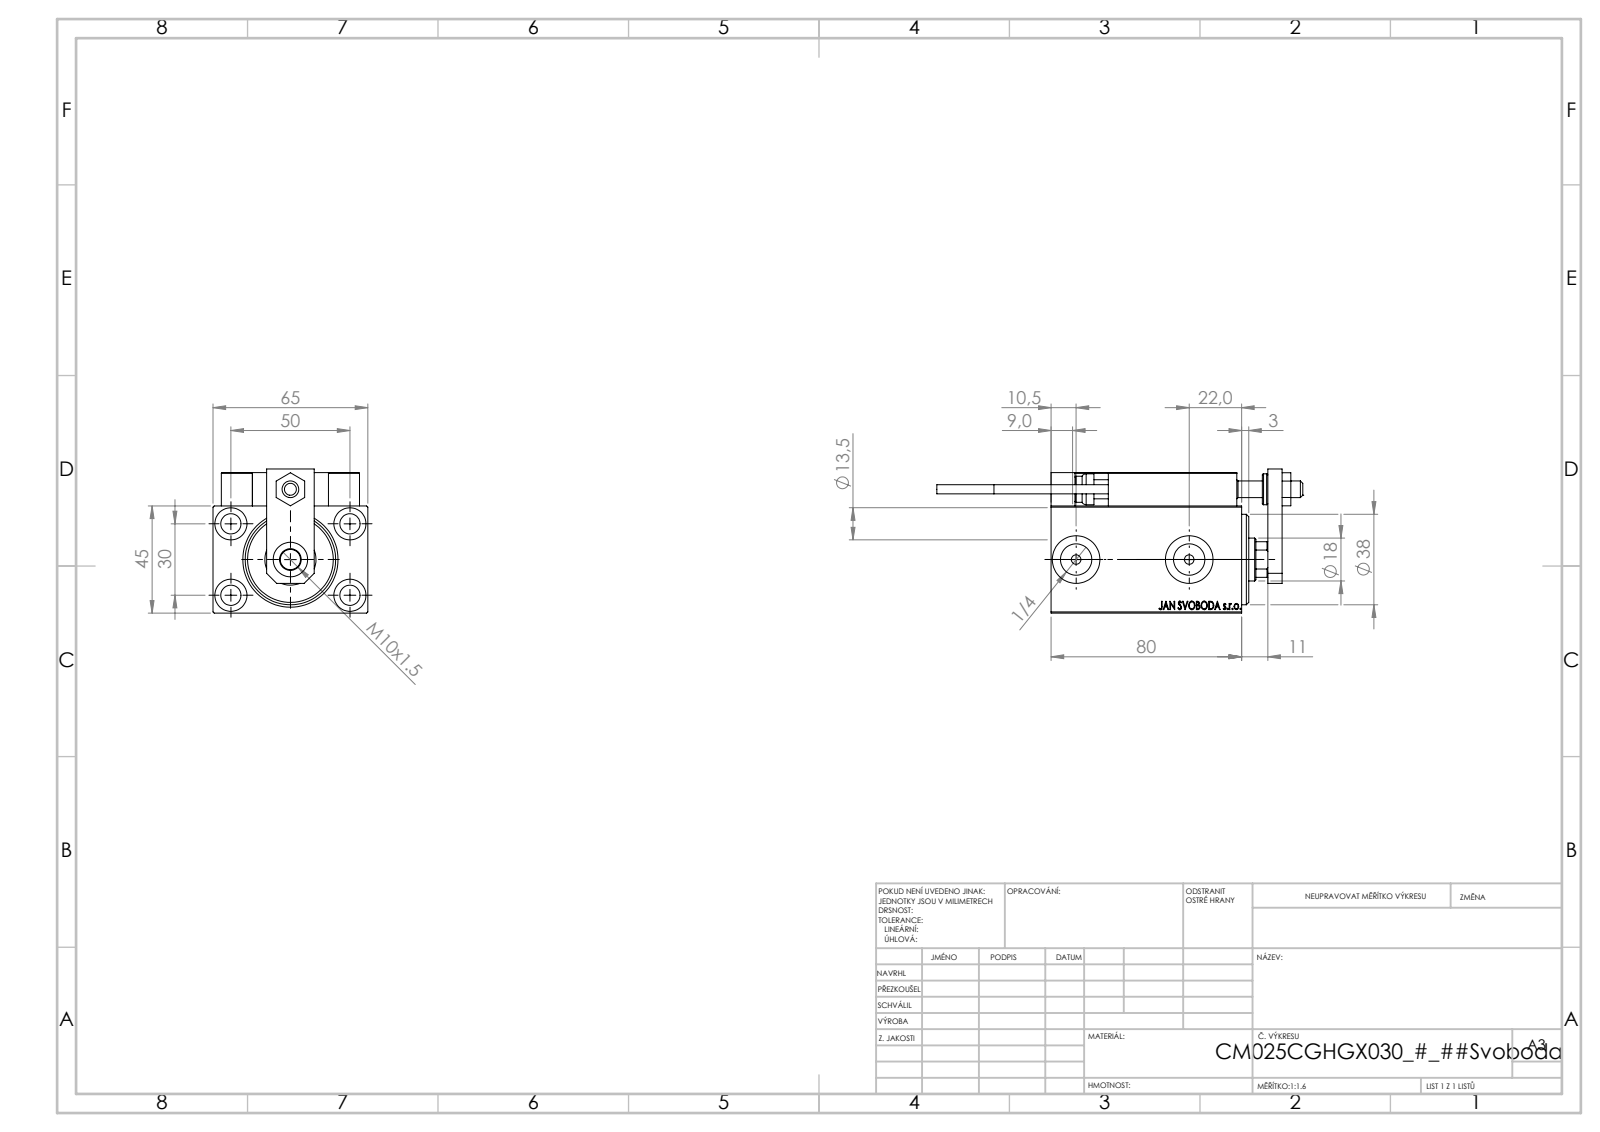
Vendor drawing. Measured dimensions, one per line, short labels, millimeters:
name: SWITCH X; ZARAZKA; V450CM_C_VCP; SWITCH DIM B,W (+7 more)
written by: SolidWorks 2019 (CONFIG_CONTROL_DESIGN)
unit: mm
bodies: 23 solids, 1282 faces (560 planar, 188 cylindrical, 534 other)
size: 153.7 × 65 × 60.5
volume: 248 224 mm³; area: 74 049 mm²
holes: 6× ⌀4, 5× ⌀8, 5× ⌀8.5, 4× ⌀3.2, 4× ⌀13.5, 2× ⌀5, 2× ⌀13.16, 2× ⌀20, 1× ⌀7, 1× ⌀14.5, 1× ⌀18, 1× ⌀21.5
bosses: 2× ⌀5, 2× ⌀3.8, 1× ⌀13, 1× ⌀11
rounds: 30× R0.3, 2× R3, 1× R8.5
face distances: 45, 65, 14, 59, 6, 3, 13, 3.5, 5, 7
hole spacings: 29.15, 11.37, 20, 28.9, 29.59, 29.69, 30, 32.06
